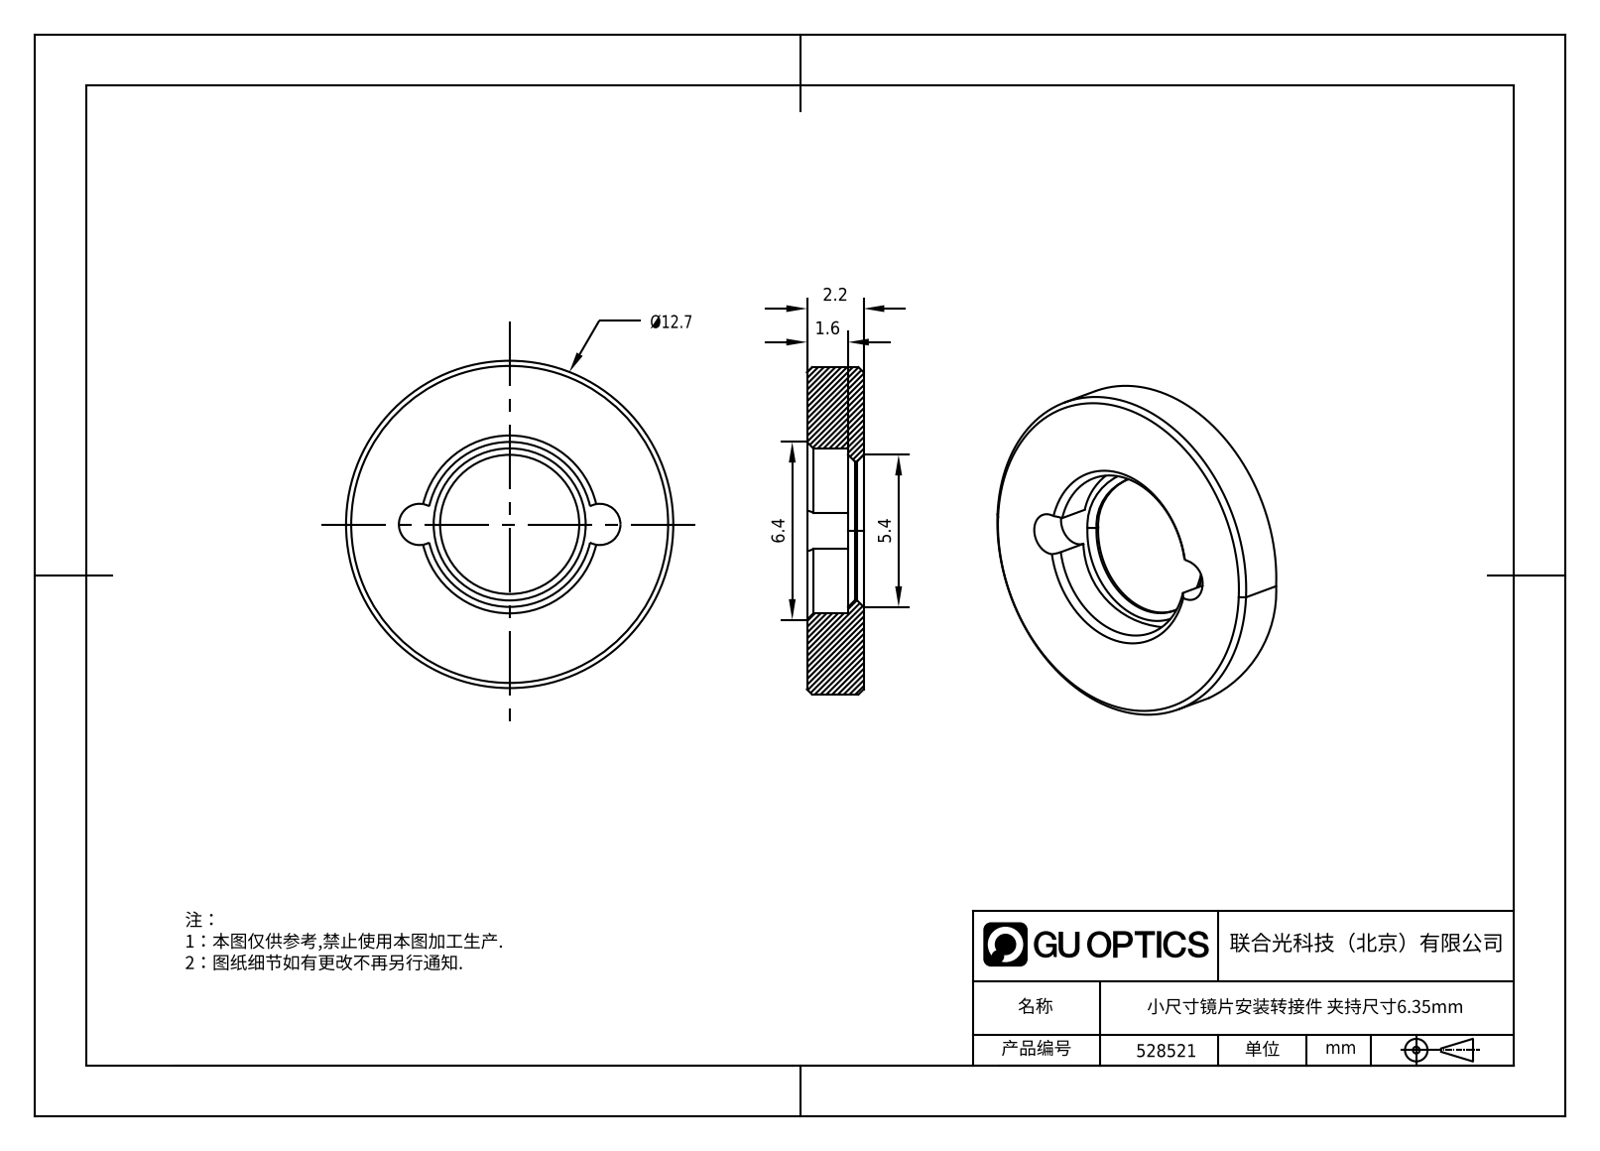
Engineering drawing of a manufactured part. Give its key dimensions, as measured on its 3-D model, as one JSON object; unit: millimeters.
{"part_name": "1.6.4.7-ZSJ-05-6.35", "step_written_by": "SolidWorks 2021 (CONFIG_CONTROL_DESIGN)", "units": "millimeters", "bodies": {"solids": 1, "faces": 22, "planar": 3, "cylindrical": 9, "other": 10}, "overall_size": [12.7, 12.7, 2.2], "volume_mm3": 205, "surface_area_mm2": 327, "round_holes": [[5.4, 1], [6.4, 1]], "round_bosses_or_shafts": [[12.7, 1]], "partial_cylinders_radius": [[0.8, 2]], "face_to_face_distances": [2.2, 0.6, 1.6]}
